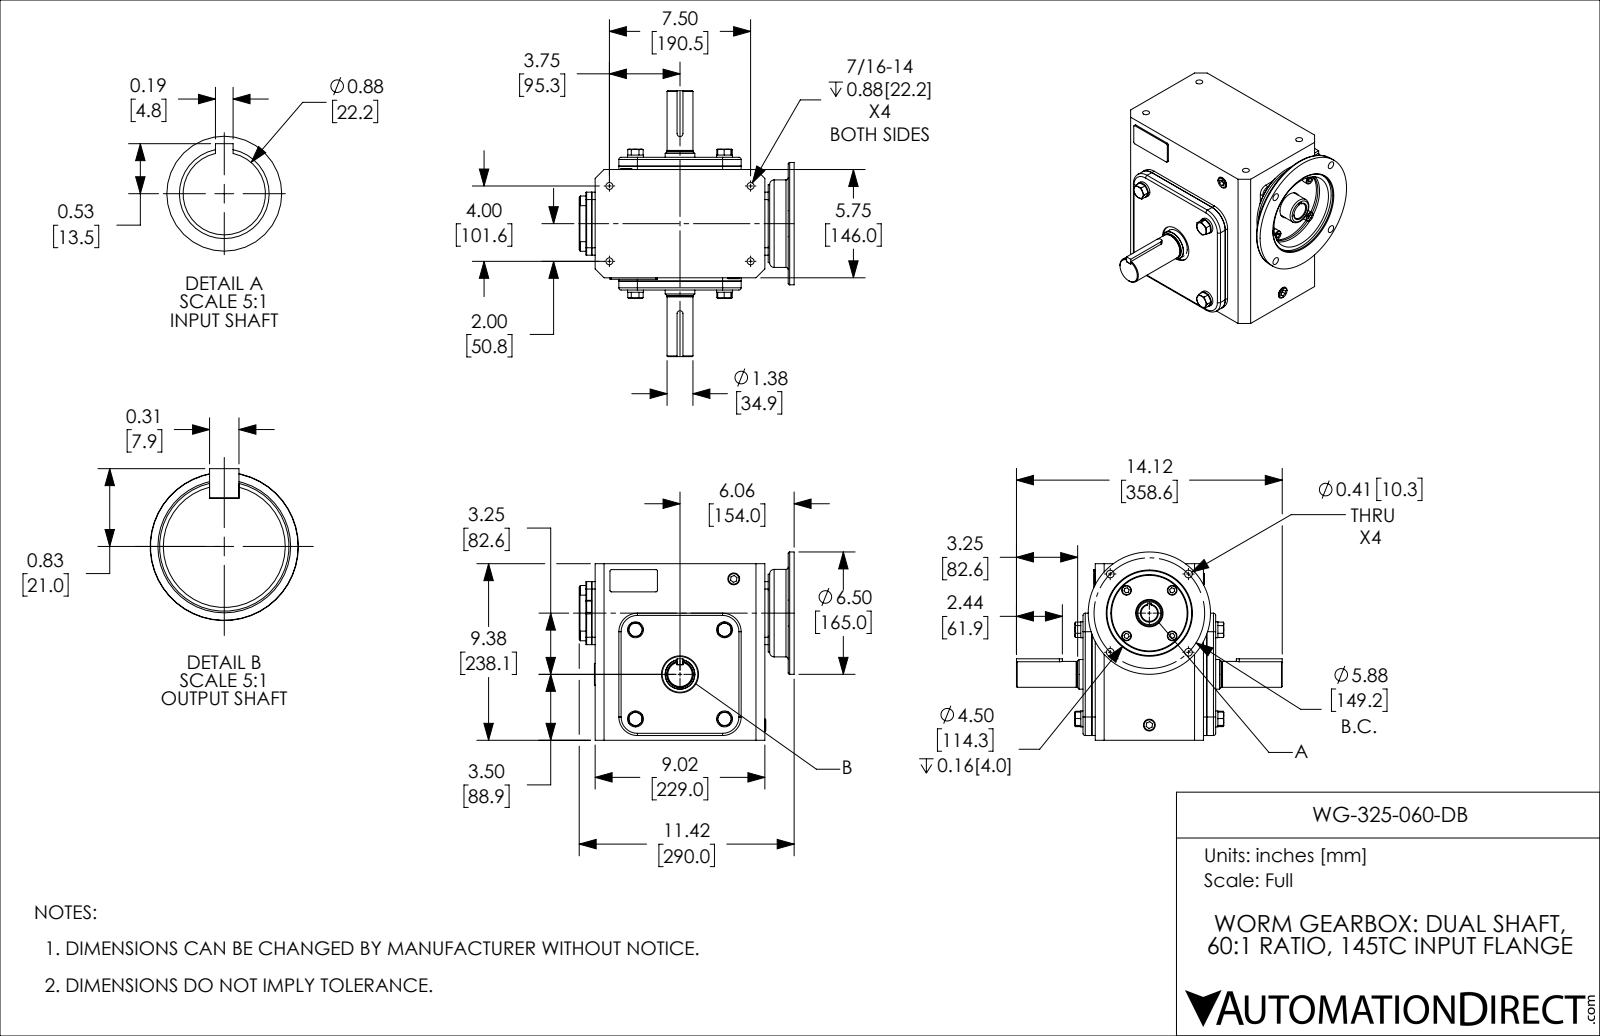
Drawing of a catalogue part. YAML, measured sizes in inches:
part_name: "WG-325-060-DB"
step_written_by: "SolidWorks 2017 (AUTOMOTIVE_DESIGN)"
units: inches
bodies: {solids: 42, faces: 612, planar: 331, cylindrical: 178, other: 103}
overall_size: [14.118, 11.417, 9.998]
volume: 516.3
surface_area: 941.7
round_holes:
  - {diameter: 0.368, count: 4}
  - {diameter: 0.406, count: 4}
  - {diameter: 0.628, count: 3}
  - {diameter: 0.591, count: 1}
  - {diameter: 0.875, count: 1}
  - {diameter: 0.978, count: 1}
  - {diameter: 1.181, count: 1}
  - {diameter: 1.457, count: 1}
  - {diameter: 1.969, count: 1}
  - {diameter: 2.441, count: 1}
  - {diameter: 2.756, count: 1}
  - {diameter: 4.016, count: 1}
round_bosses_or_shafts:
  - {diameter: 0.846, count: 4}
  - {diameter: 0.512, count: 4}
  - {diameter: 6.496, count: 1}
  - {diameter: 4.646, count: 1}
  - {diameter: 4.134, count: 1}
  - {diameter: 2.835, count: 1}
  - {diameter: 1.575, count: 1}
  - {diameter: 1.378, count: 1}
partial_cylinders:
  - {radius: 0.118, count: 8}
  - {radius: 0.079, count: 7}
  - {radius: 0.394, count: 4}
  - {radius: 0.906, count: 4}
  - {radius: 0.984, count: 4}
  - {radius: 0.02, count: 2}
  - {radius: 0.039, count: 2}
  - {radius: 0.156, count: 2}
face_to_face_distances: [0.079, 0.177, 6.496, 0.394, 6.969, 0.472, 6.575, 6.398, 0.571, 0.65]
hole_center_spacings: [2.937, 4.154, 2.385, 4, 4.389, 5.718, 5.817, 5.875]
